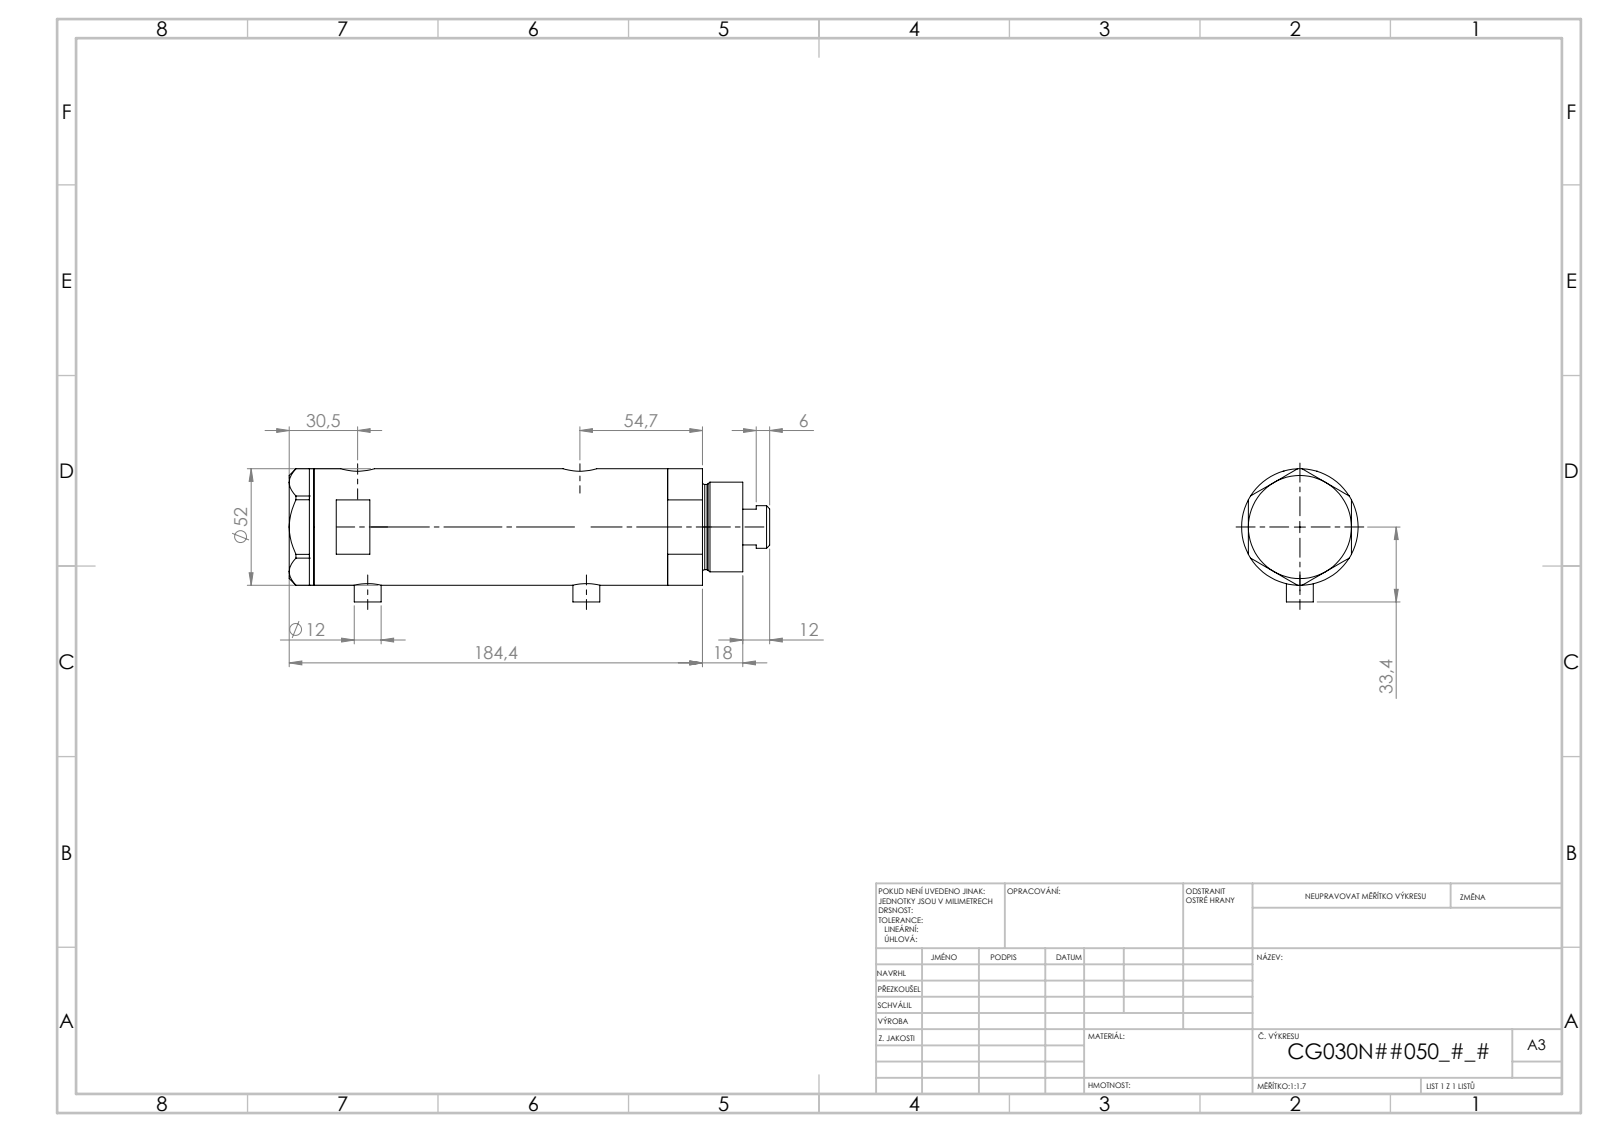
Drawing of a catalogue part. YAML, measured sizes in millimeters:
part_name: "V270CG_VC; V270CG_MIDDLE; V270CG_FRONT; V270CG_BACK"
step_written_by: "SolidWorks 2019 (CONFIG_CONTROL_DESIGN)"
units: millimeters
bodies: {solids: 4, faces: 140, planar: 67, cylindrical: 53, other: 20}
overall_size: [199.02, 53.1, 52]
volume: 354070
surface_area: 81112
round_holes:
  - {diameter: 5, count: 2}
  - {diameter: 9.73, count: 2}
  - {diameter: 12.5, count: 2}
  - {diameter: 15, count: 2}
  - {diameter: 6.5, count: 1}
  - {diameter: 20, count: 1}
  - {diameter: 21.5, count: 1}
  - {diameter: 30, count: 1}
  - {diameter: 33, count: 1}
  - {diameter: 44, count: 1}
round_bosses_or_shafts:
  - {diameter: 12, count: 2}
  - {diameter: 52, count: 1}
  - {diameter: 40, count: 1}
  - {diameter: 38, count: 1}
  - {diameter: 19, count: 1}
face_to_face_distances: [103.54, 23.8, 79.74, 11, 34.8, 114.54, 46, 150.94, 139.94, 116.14]
hole_center_spacings: [2.9, 4.5, 76.75, 79.65, 81.25, 84.15, 2.89, 2.91]
